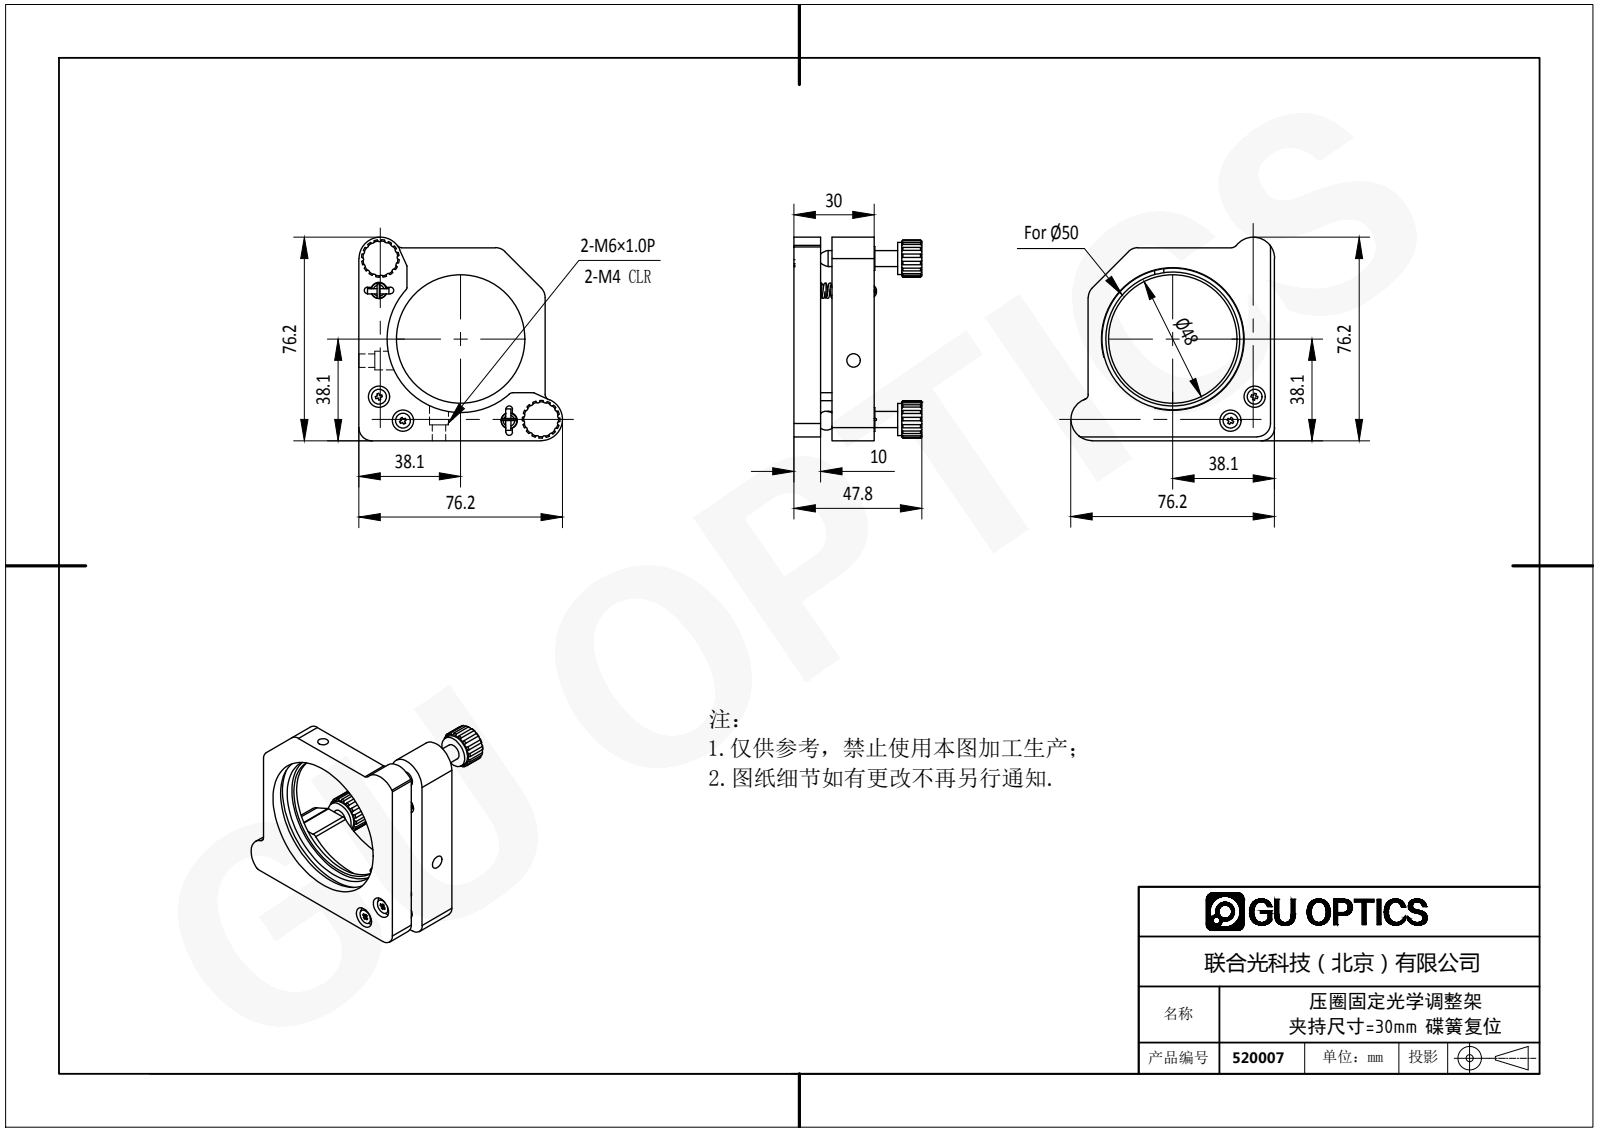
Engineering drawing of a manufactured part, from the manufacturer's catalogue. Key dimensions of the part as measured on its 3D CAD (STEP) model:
Part name (STEP PRODUCT): 520007
STEP written by: SolidWorks 2016 (AUTOMOTIVE_DESIGN)
Units: millimetres
Bodies: 0 solids, 586 faces (196 planar, 193 cylindrical, 197 other)
Overall size (bounding box): 76.2 × 76.2 × 47.8
Round holes (diameter × count): ⌀6 ×4, ⌀8 ×4, ⌀4 ×3, ⌀5 ×2, ⌀7.5 ×2, ⌀48 ×1, ⌀50 ×1, ⌀53 ×1, ⌀55 ×1
Round bosses / shafts (diameter × count): ⌀12 ×2, ⌀9 ×2, ⌀5.4 ×2, ⌀3 ×2, ⌀2 ×2, ⌀0.8 ×2
Partial cylindrical surfaces — rounded edges, fillets, slot ends (radius × count): R0.75 ×32, R1 ×5, R1.25 ×4, R5 ×4, R2 ×3, R7 ×2, R8 ×2
Main face-to-face distances: 10, 4.2, 14.2, 15.8, 20, 30, 1.5, 6, 4, 2.5
Hole centre spacings: 12.01, 35.55, 37.46, 39.7, 42.57, 49.52, 51.7, 61.29
